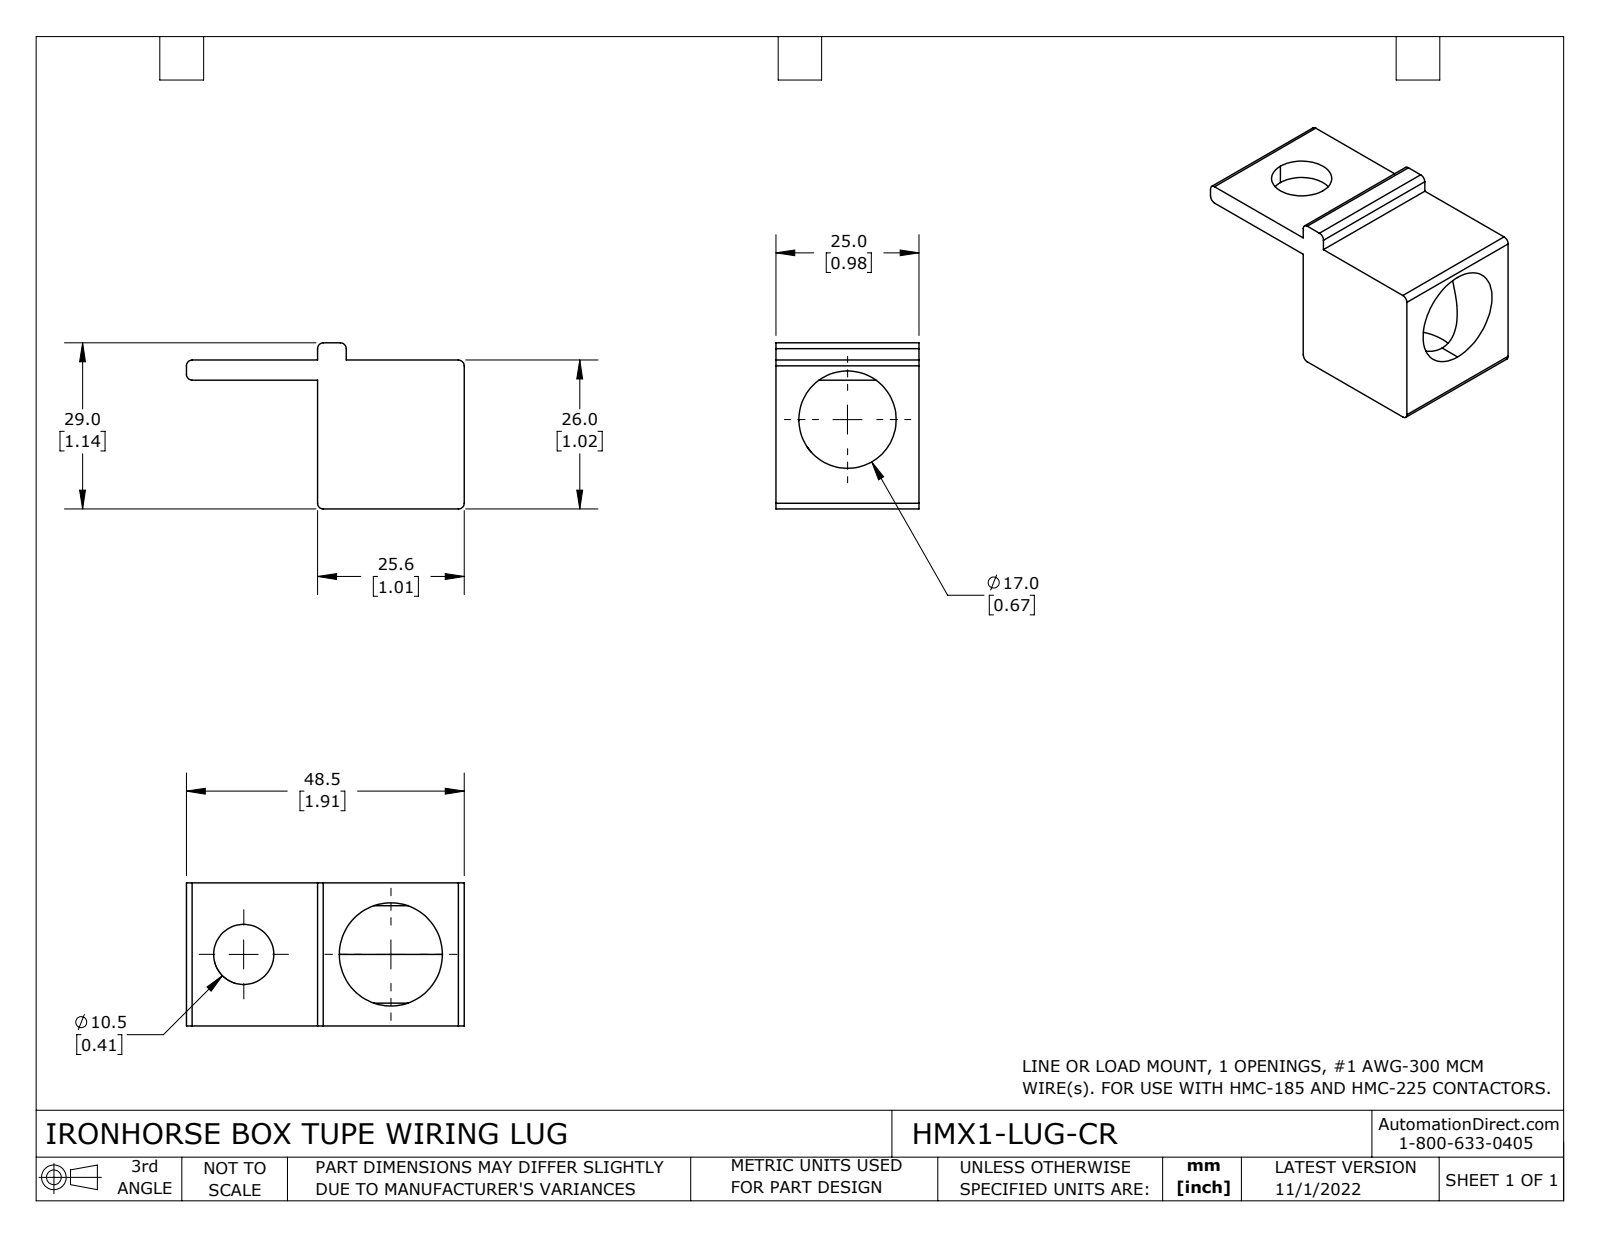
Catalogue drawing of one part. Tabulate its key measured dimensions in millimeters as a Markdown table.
| quantity | value |
| --- | --- |
| part name | HMX1-LUG-CR |
| STEP written by | SolidWorks 2021 (CONFIG_CONTROL_DESIGN) |
| units | millimeters |
| bodies | 1 solid, 28 faces (15 planar, 13 cylindrical, 0 other) |
| overall size | 48.5 × 29 × 25 |
| volume | 10 700 mm³ |
| surface area | 6 212 mm² |
| round holes (diameter × count) | 10.5 × 1, 17 × 1, 18 × 1 |
| partial cylindrical surfaces (radius × count) | 1 × 7 |
| main face-to-face distances | 25, 3.5, 25.6, 26, 22.5, 3, 6.5, 29, 5, 20.6 |
| hole center spacings | 25.7 |
